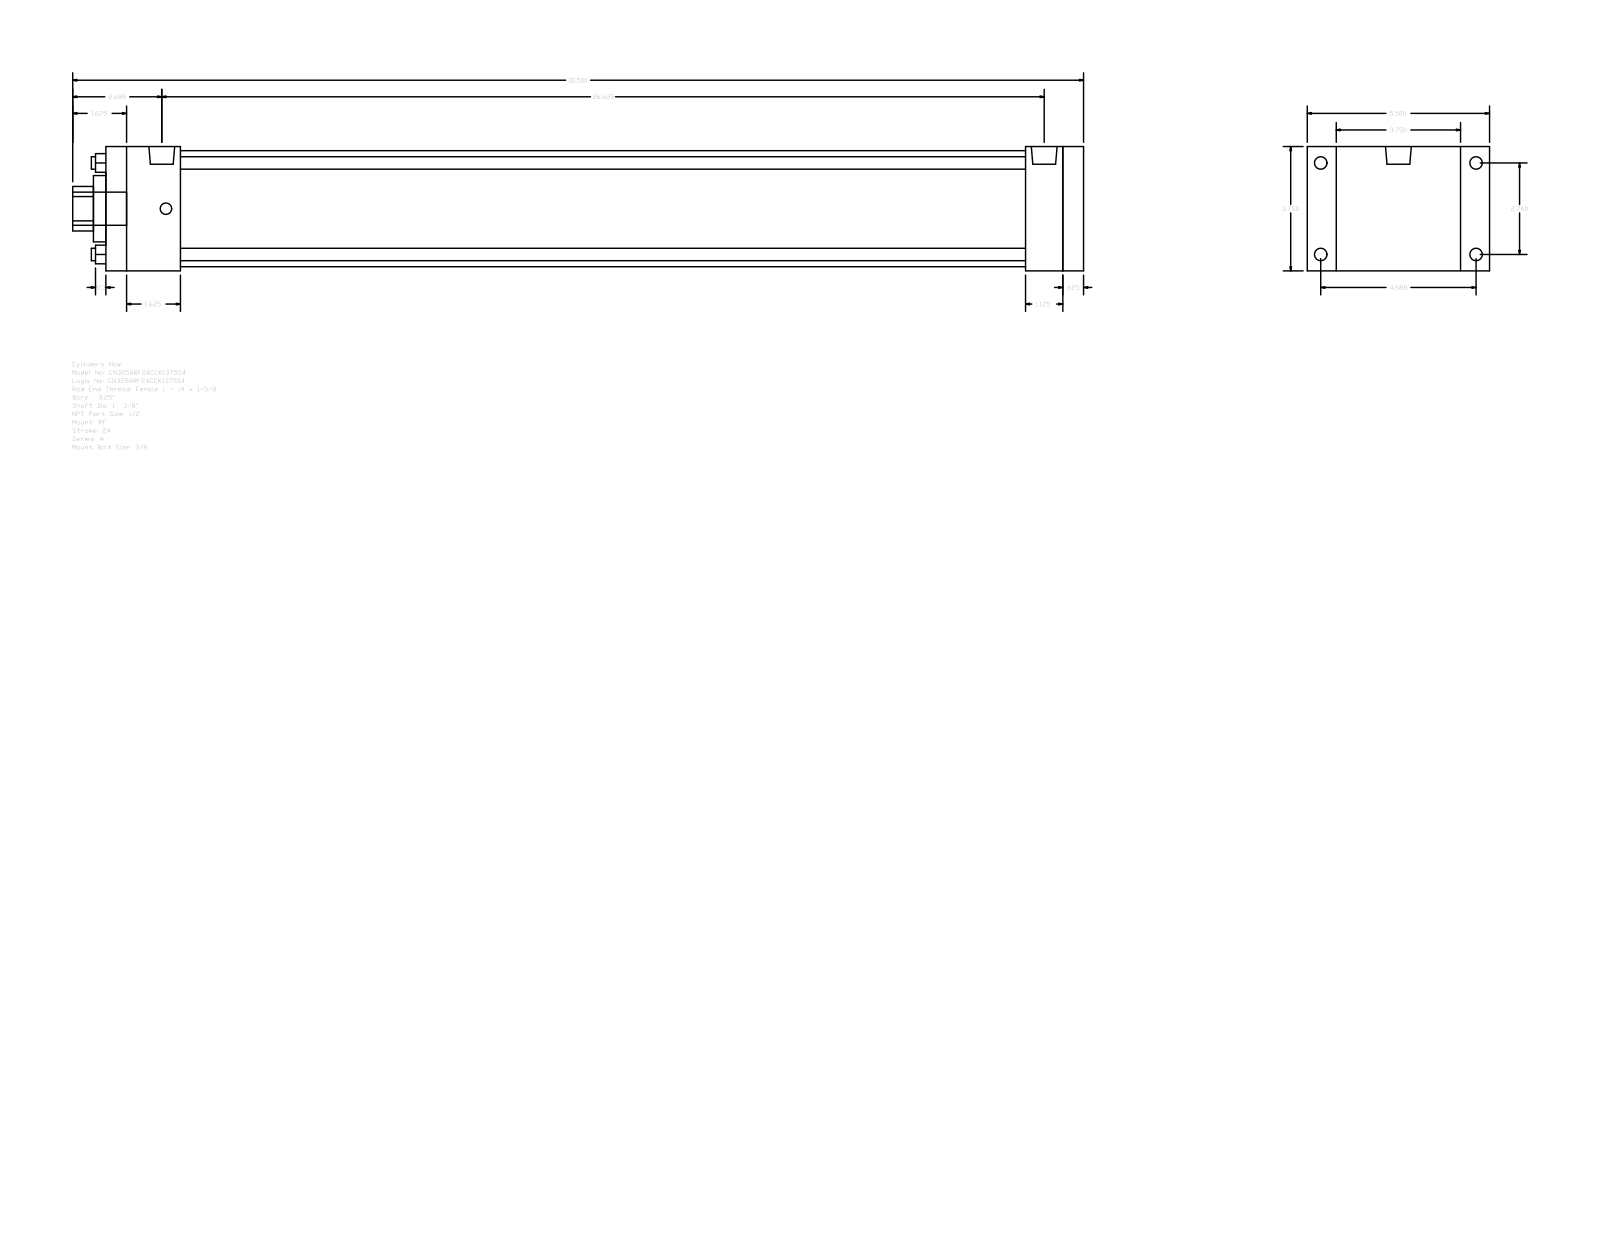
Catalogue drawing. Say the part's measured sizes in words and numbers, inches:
The part is named "A_RF__0325_1.375". Its 3-D file was written by "GSSL Pune (CONFIG_CONTROL_DESIGN)". It is 0 solids with 92 faces: 64 planar, 28 cylindrical and 0 other. Overall it measures 30.5 by 5.5 by 3.75 inches. Round holes: 4 of diameter 0.375, 1 of diameter 1.375, 1 of diameter 2, 1 of diameter 3.5. Round bosses or shafts: 4 of diameter 0.375, 4 of diameter 0.344, 2 of diameter 0.778, 1 of diameter 1. Partial cylindrical surfaces (rounded edges, fillets, slot ends): 1 of radius 0.672. The main face-to-face distances are 3.75, 29.5, 0.625, 28.875, 1.125, 0.875, 4.625, 27.75, 1.75, 2.25. The hole center spacings are 1.952, 2.76, 3.903.
